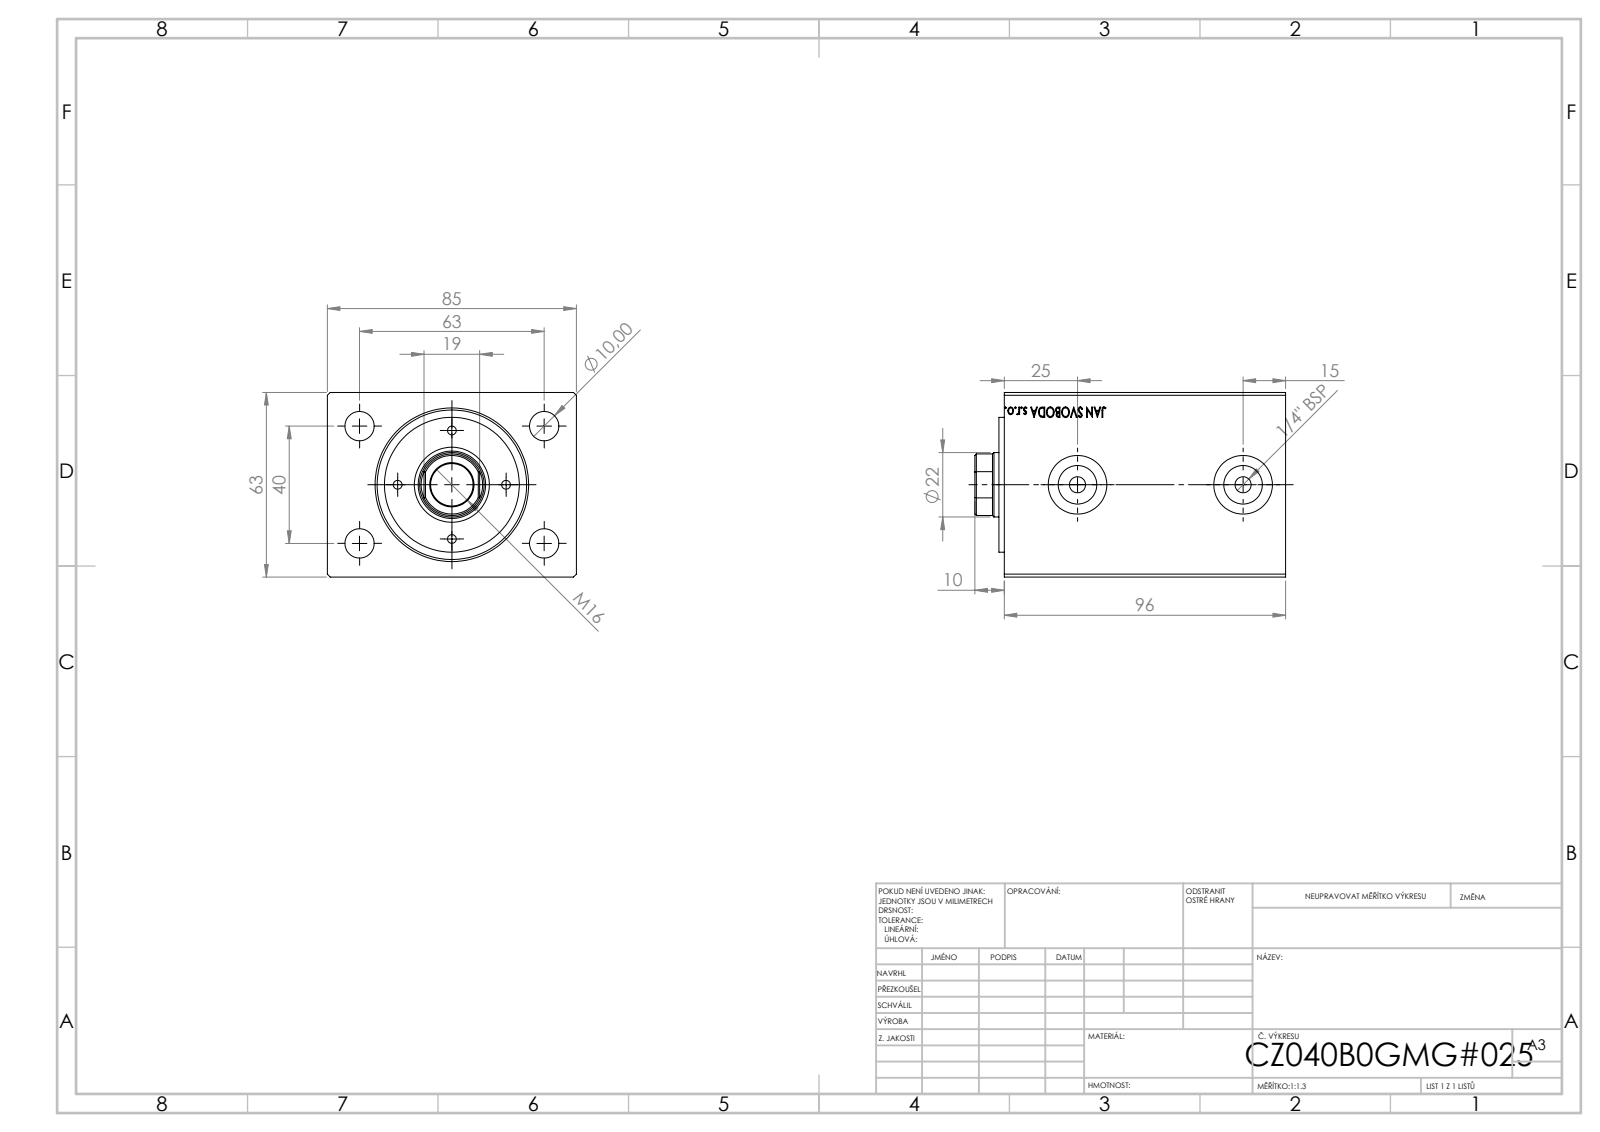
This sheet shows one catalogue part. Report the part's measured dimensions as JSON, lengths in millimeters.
{"part_name": "V500CZ; V500CZ_B_VC", "step_written_by": "SolidWorks 2019 (CONFIG_CONTROL_DESIGN)", "units": "millimeters", "bodies": {"solids": 3, "faces": 873, "planar": 399, "cylindrical": 58, "other": 416}, "overall_size": [106, 85, 63], "volume_mm3": 511561, "surface_area_mm2": 90597, "round_holes": [[3, 4], [10, 4], [5.5, 2], [13.16, 2], [20, 2], [14.5, 1], [22, 1], [23, 1], [36, 1], [40, 1], [51, 1]], "round_bosses_or_shafts": [[46, 1]], "partial_cylinders_radius": [[10.5, 1]], "face_to_face_distances": [63, 85, 96, 81.3, 14.7, 71, 10.3, 25, 1.8, 72.8], "hole_center_spacings": [18.5, 23.85, 26.16, 31.54, 37.31, 49.74, 53.85, 37]}
